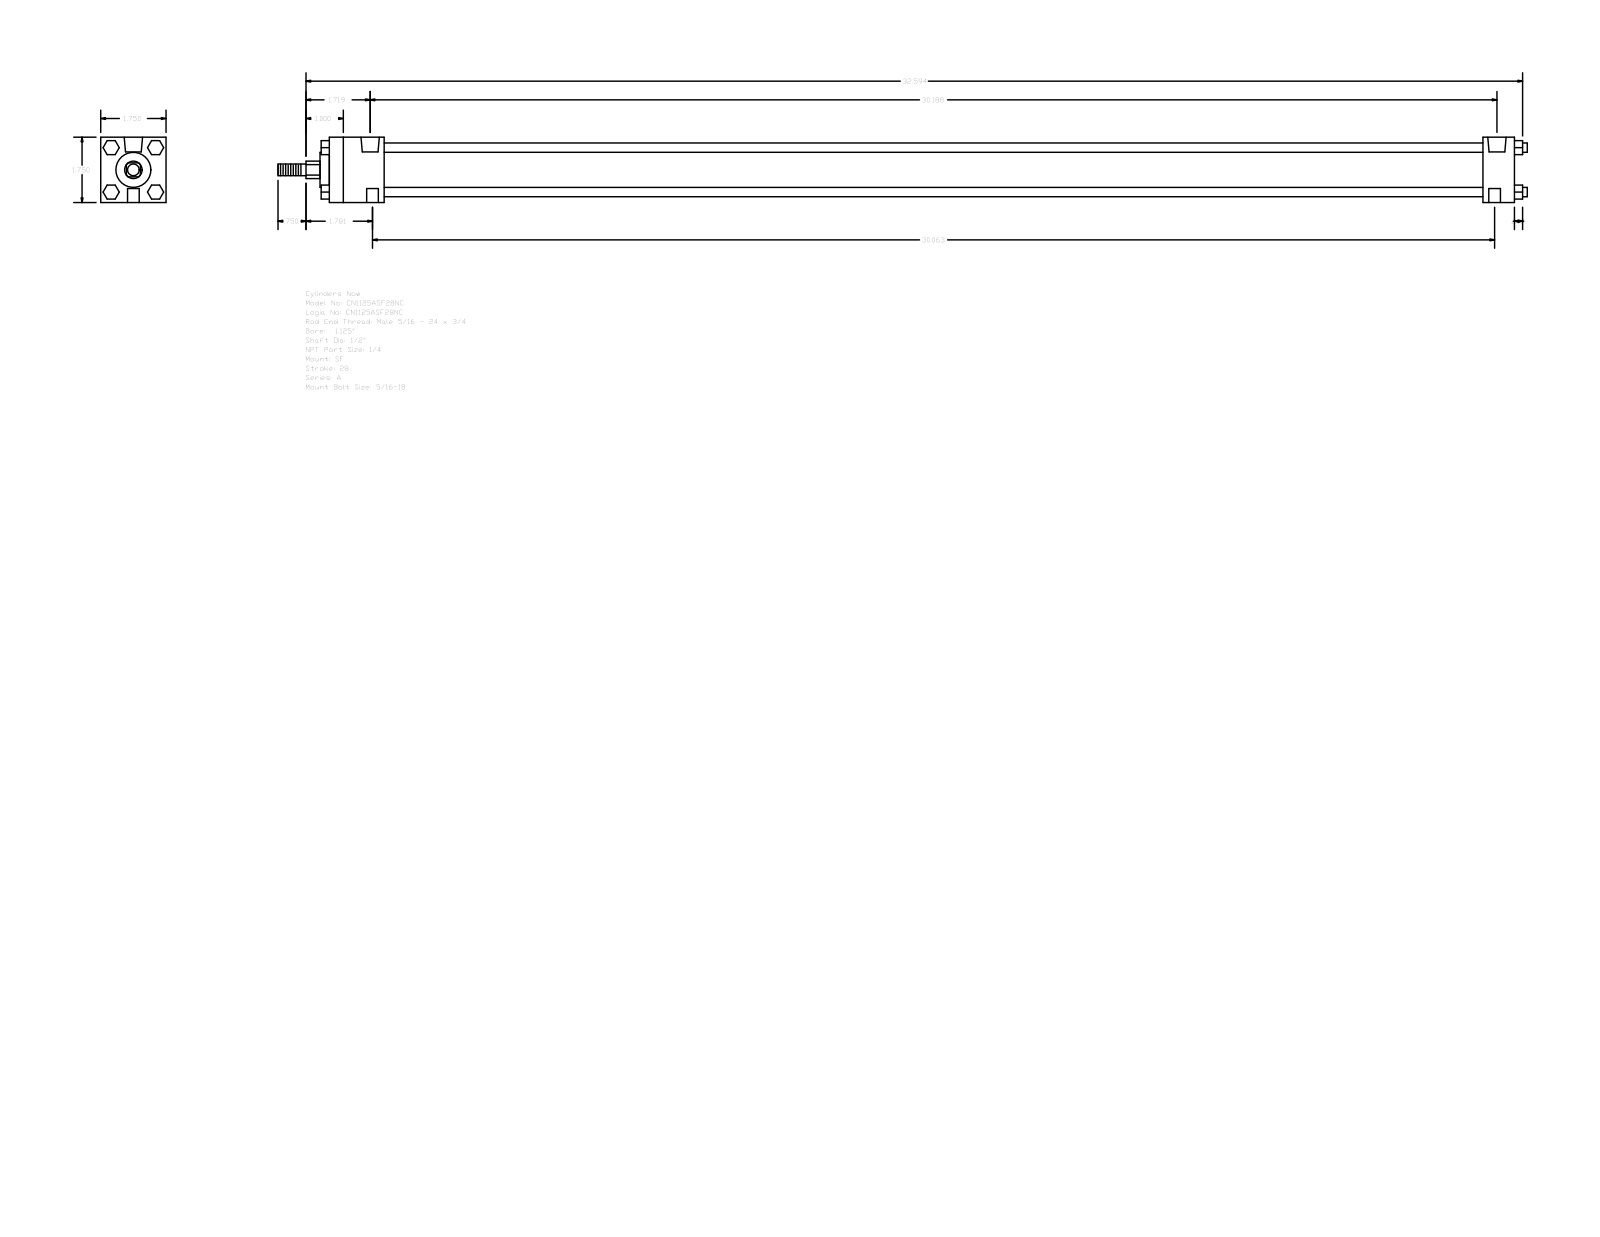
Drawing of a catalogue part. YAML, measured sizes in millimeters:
part_name: "A_SF__0112_0.5"
step_written_by: "GSSL Pune (CONFIG_CONTROL_DESIGN)"
units: millimeters
bodies: {solids: 0, faces: 120, planar: 92, cylindrical: 28, other: 0}
overall_size: [850.11, 44.45, 44.45]
round_holes:
  - {diameter: 5.56, count: 2}
  - {diameter: 7.94, count: 2}
  - {diameter: 12.49, count: 2}
round_bosses_or_shafts:
  - {diameter: 6.35, count: 4}
  - {diameter: 31.88, count: 1}
  - {diameter: 23.81, count: 1}
  - {diameter: 12.7, count: 1}
  - {diameter: 7.94, count: 1}
partial_cylinders:
  - {radius: 5.94, count: 1}
face_to_face_distances: [44.46, 806.45, 785.01, 21.44, 37.3, 747.71, 769.15, 9.53, 5.59, 26.99]
hole_center_spacings: [763.59, 1.58, 1.59, 765.17, 765.18, 766.76]
